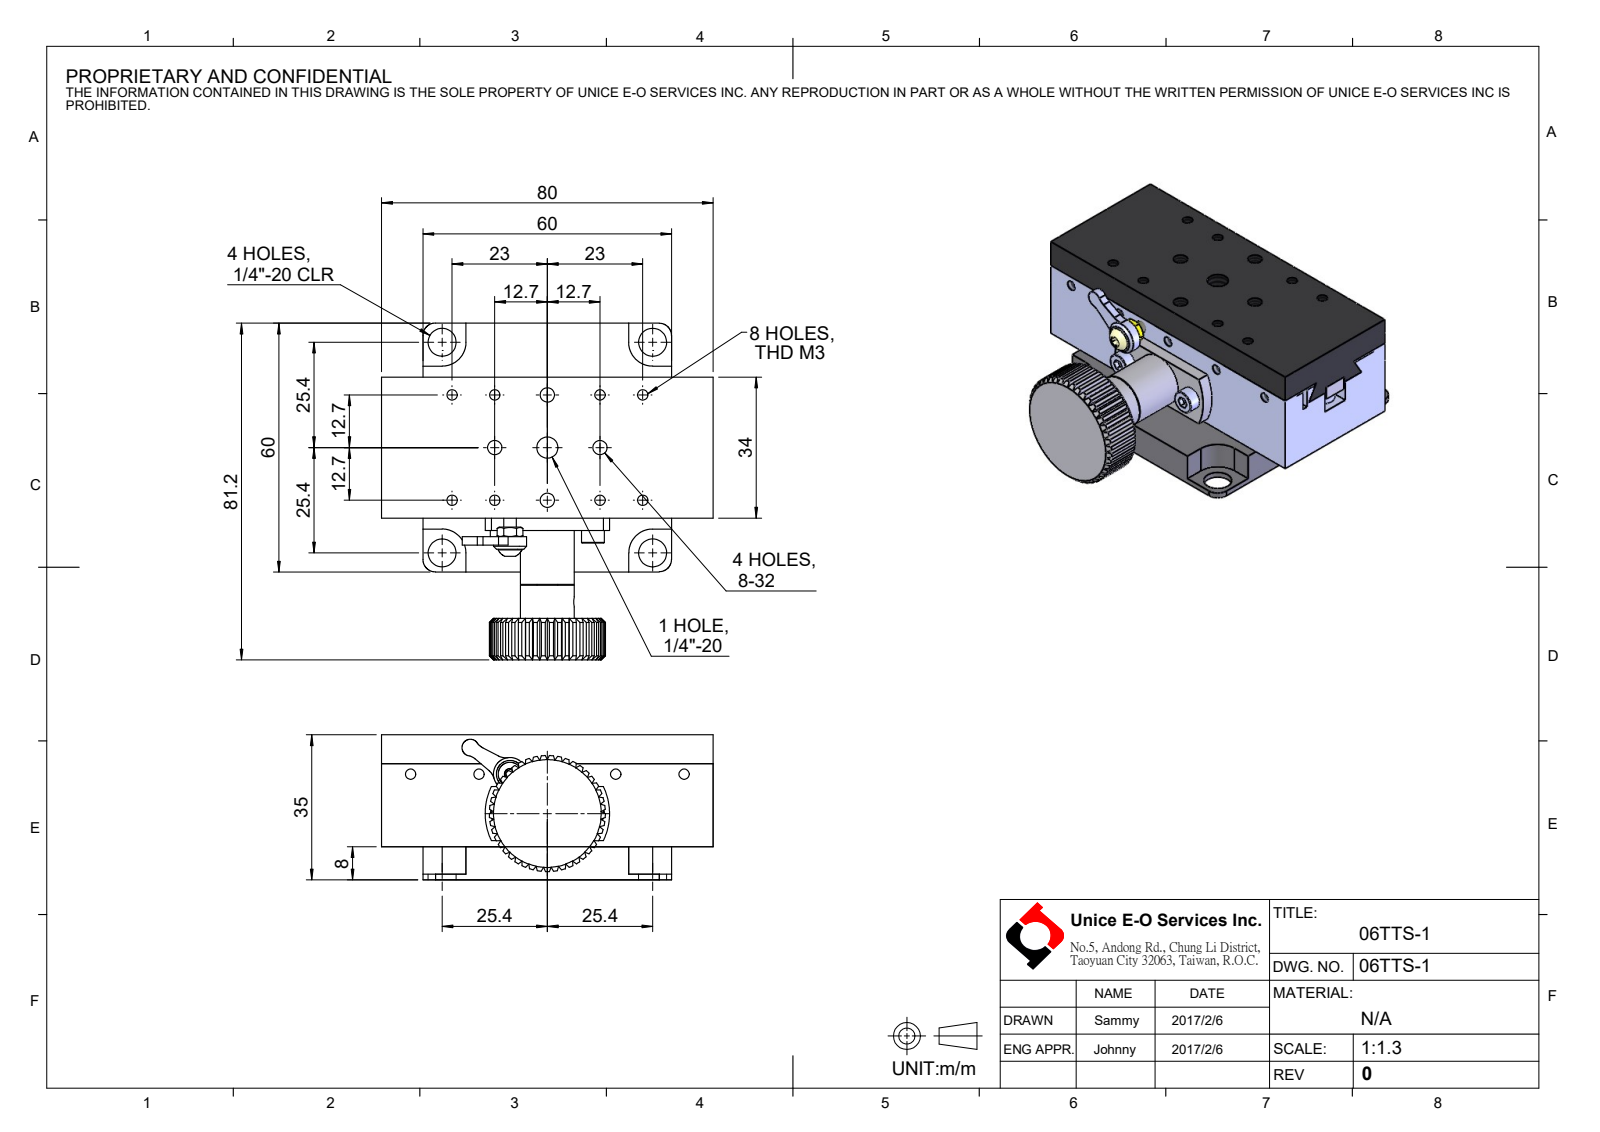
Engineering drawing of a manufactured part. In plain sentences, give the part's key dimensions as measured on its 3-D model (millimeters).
The part is named "06TTS-1". Its 3-D file was written by "SolidWorks 2016 (CONFIG_CONTROL_DESIGN)". It is 24 solids with 1762 faces: 1045 planar, 319 cylindrical and 398 other. Overall it measures 81.2 by 80 by 35 millimeters. Its volume is 104 961 cubic millimeters and its surface area 43 637 square millimeters. Round holes: 25 of diameter 2.5, 6 of diameter 3.4, 6 of diameter 6.5, 4 of diameter 3.45, 4 of diameter 6.76, 2 of diameter 2.05, 2 of diameter 3, 2 of diameter 4, 1 of diameter 3.5, 1 of diameter 5, 1 of diameter 5.1, 1 of diameter 5.11. Round bosses or shafts: 10 of diameter 5.5, 9 of diameter 3, 2 of diameter 8, 1 of diameter 13, 1 of diameter 5.7, 1 of diameter 4. Partial cylindrical surfaces (rounded edges, fillets, slot ends): 4 of radius 3, 4 of radius 4, 4 of radius 5.75, 1 of radius 2, 1 of radius 2.25, 1 of radius 14, 1 of radius 15. The main face-to-face distances are 8, 7, 20, 27, 10, 28, 35, 4.5, 23.5, 34. The hole center spacings are 12.5, 12.7, 28.4, 17.96, 27.95, 25, 25.2, 17.68.
